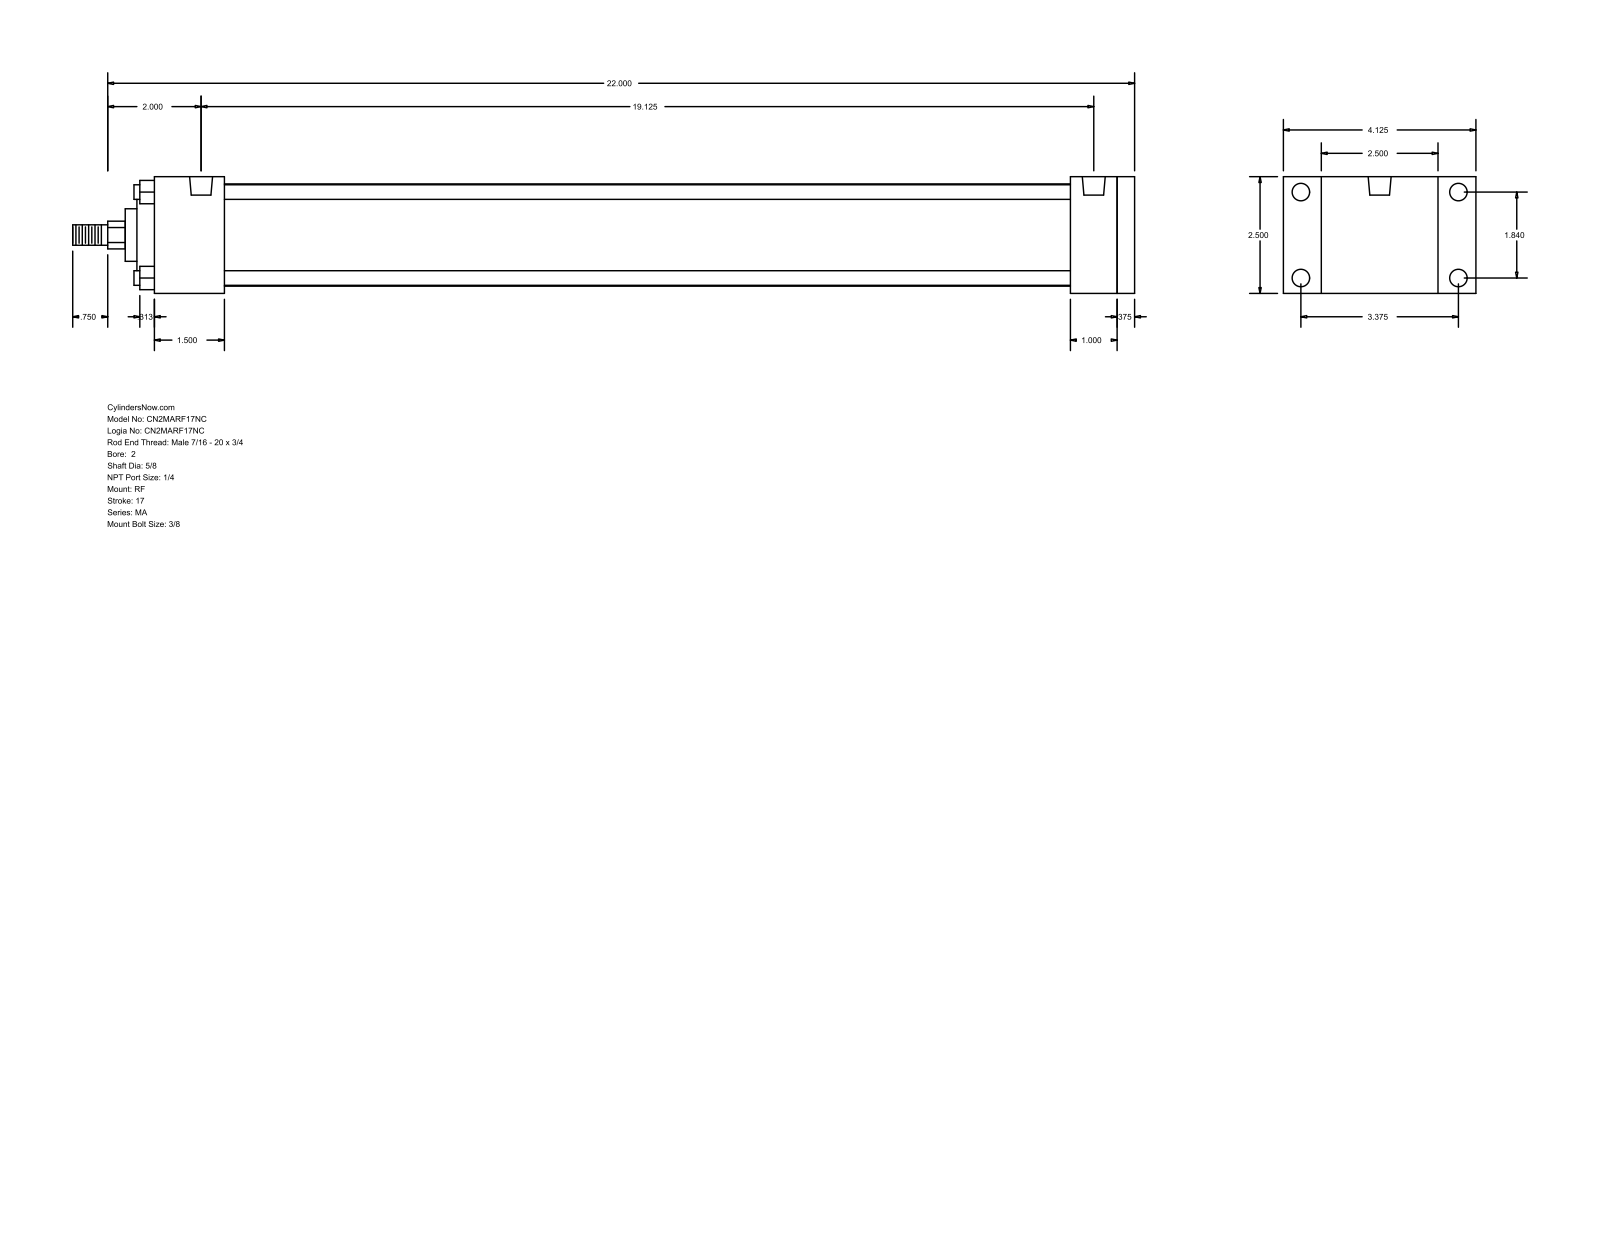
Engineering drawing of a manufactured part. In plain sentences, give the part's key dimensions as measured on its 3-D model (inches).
The part is named "MA_RF__0200_0.625". Its 3-D file was written by "GSSL Pune (CONFIG_CONTROL_DESIGN)". It is 0 solids with 94 faces: 65 planar, 29 cylindrical and 0 other. Overall it measures 22.75 by 4.125 by 2.5 inches. Round holes: 4 of diameter 0.313, 4 of diameter 0.375, 2 of diameter 0.492. Round bosses or shafts: 4 of diameter 0.313, 1 of diameter 2.19, 1 of diameter 2, 1 of diameter 1.125, 1 of diameter 0.625, 1 of diameter 0.437. Partial cylindrical surfaces (rounded edges, fillets, slot ends): 1 of radius 0.297. The main face-to-face distances are 2.5, 0.375, 1.5, 20.625, 21, 21.375, 19.125, 19.5, 19.625, 18.125. The hole center spacings are 1.84, 3.375, 3.844, 19.125.
